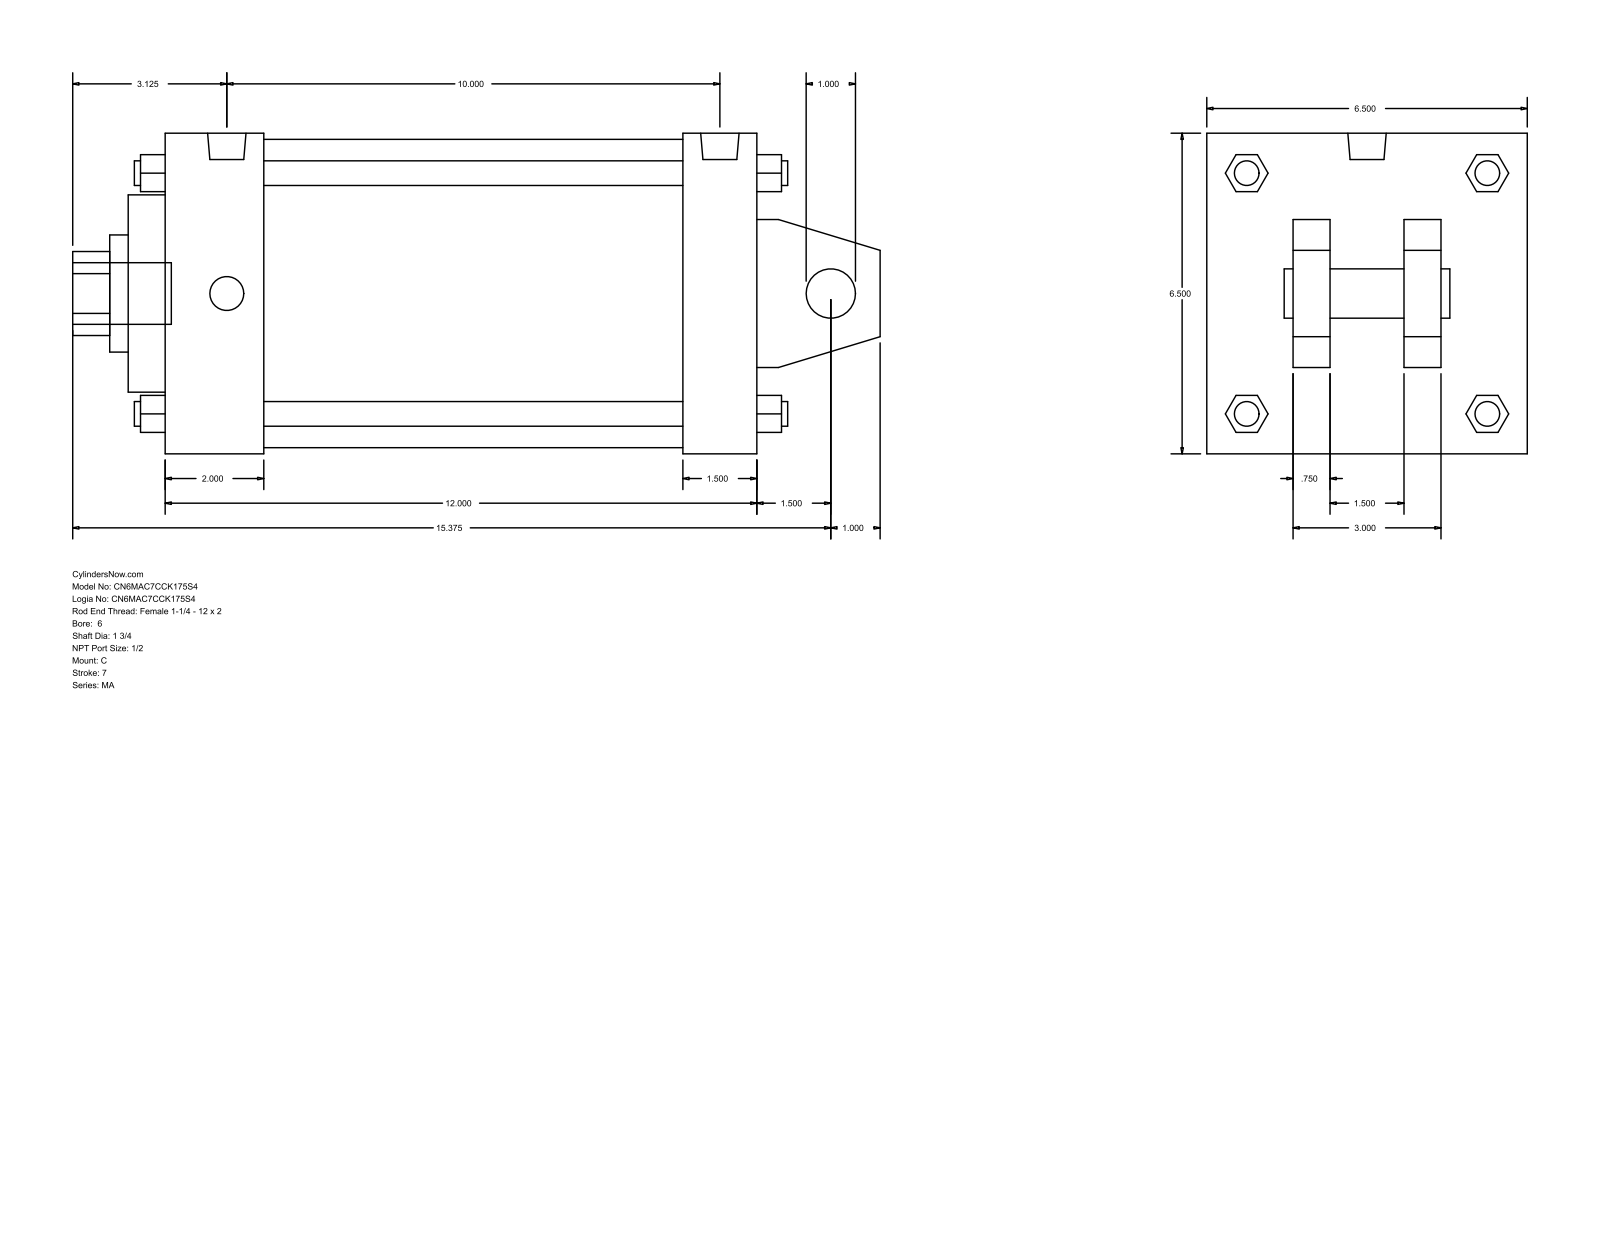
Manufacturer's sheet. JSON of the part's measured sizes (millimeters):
{"part_name": "MA_C__0600_1.75", "step_written_by": "GSSL Pune (CONFIG_CONTROL_DESIGN)", "units": "millimeters", "bodies": {"solids": 0, "faces": 141, "planar": 109, "cylindrical": 32, "other": 0}, "overall_size": [415.93, 165.1, 165.1], "round_holes": [[25.4, 1], [44.45, 1], [60.33, 1], [101.6, 1], [158.75, 1]], "round_bosses_or_shafts": [[17.46, 4], [12.7, 4], [19.77, 2], [31.75, 1]], "partial_cylinders_radius": [[21.63, 1]], "face_to_face_distances": [165.1, 304.81, 19.05, 63.5, 101.6, 50.8, 44.45, 120.65, 266.7, 57.15]}
